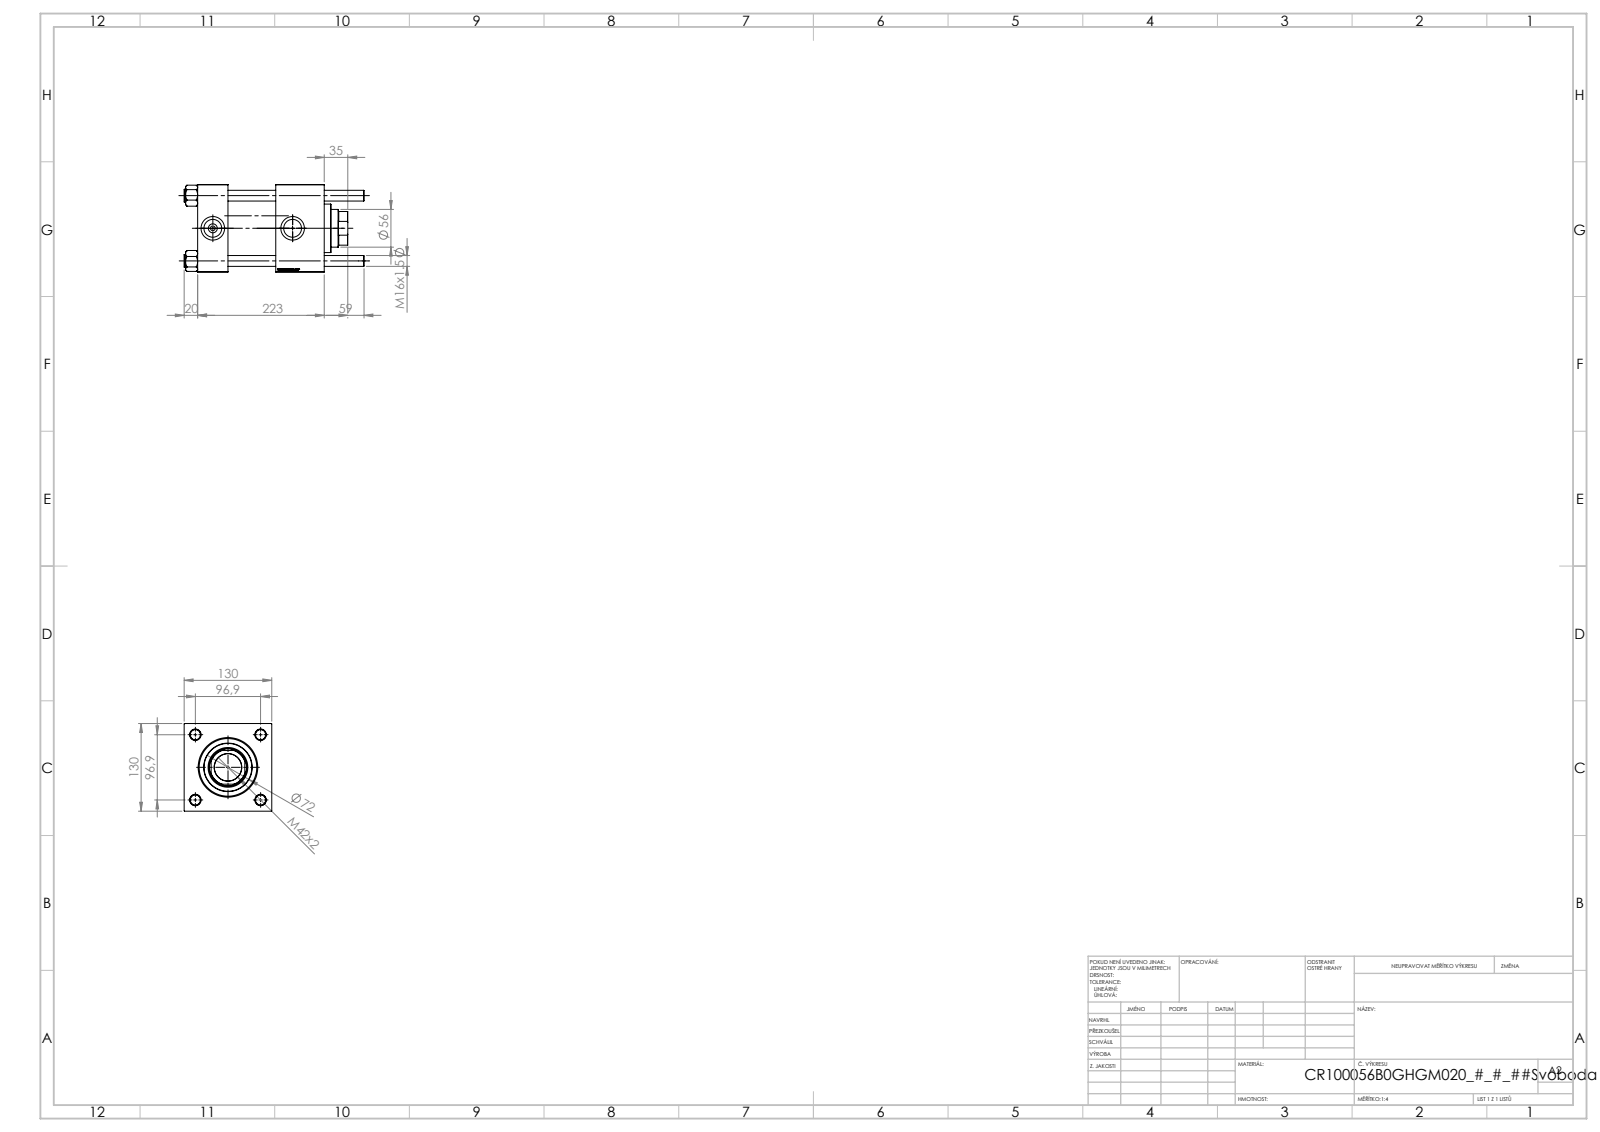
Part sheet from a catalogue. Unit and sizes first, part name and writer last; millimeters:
Units: millimetres
Overall size (bounding box): 267 × 130 × 130
Round holes (diameter × count): ⌀16 ×4, ⌀7 ×2, ⌀26.44 ×2, ⌀35 ×2, ⌀40.5 ×1, ⌀56 ×1, ⌀59 ×1, ⌀76 ×1, ⌀85.5 ×1, ⌀100 ×1
Round bosses / shafts (diameter × count): ⌀19 ×4, ⌀106 ×1, ⌀72 ×1
Partial cylindrical surfaces — rounded edges, fillets, slot ends (radius × count): R27 ×1
Main face-to-face distances: 130, 45, 188, 143, 116, 71, 72, 20, 51, 96
Hole centre spacings: 68.52, 96.9, 137.04, 118.5
Volume: 2 555 000 mm³ · Surface area: 360 341 mm²
Bodies: 11 solids, 1206 faces (480 planar, 78 cylindrical, 648 other)
Part name (STEP PRODUCT): V215_VC_A; NUT_M5_B; V215CR_B-1; V215CR_B_TYCINKA (+1 more)
STEP written by: SolidWorks 2019 (CONFIG_CONTROL_DESIGN)
